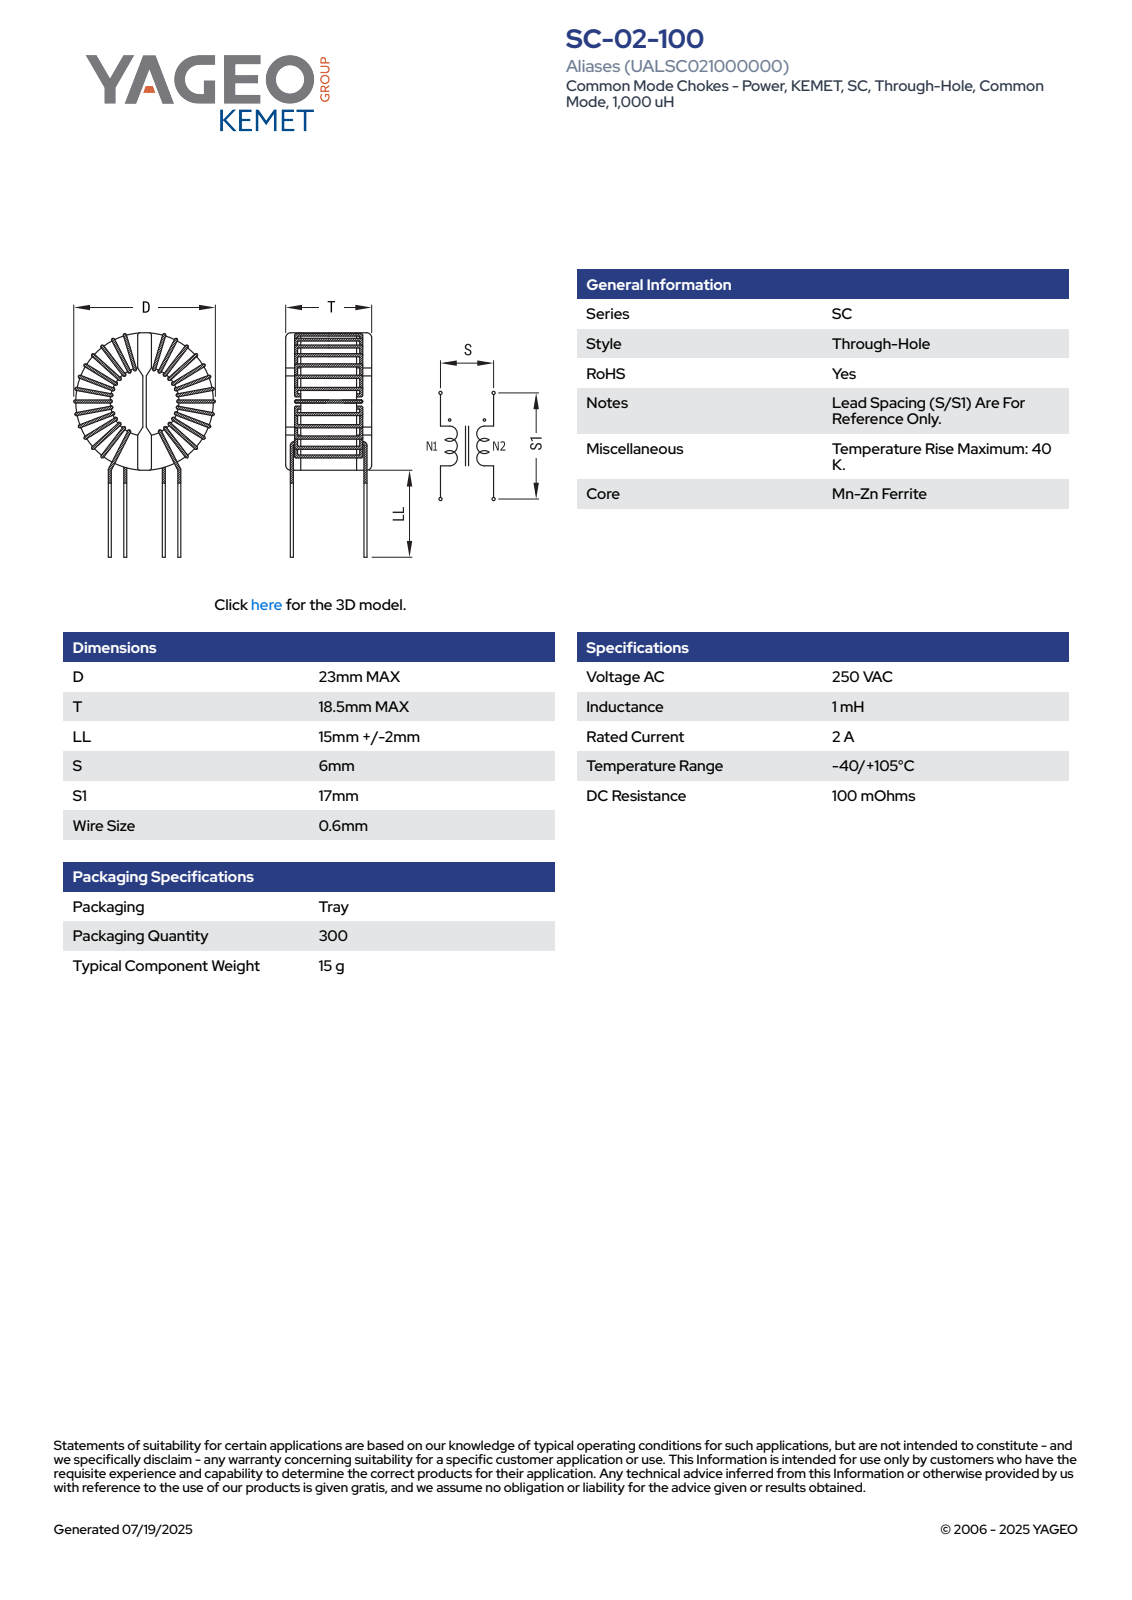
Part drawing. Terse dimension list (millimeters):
name: SC-02-100
written by: SolidWorks 2018 (AUTOMOTIVE_DESIGN)
unit: mm
bodies: 1 solid, 209 faces (62 planar, 79 cylindrical, 68 other)
size: 36.37 × 23 × 18.5
volume: 5 914 mm³; area: 3 520 mm²
bosses: 8× ⌀0.6
rounds: 16× R0.3, 4× R0.2, 1× R2.85, 1× R4.15, 1× R4.65, 1× R4.75, 1× R4.9, 1× R9.25
face distances: 16.3, 1.2, 2, 0.8, 1.1, 3.2, 17.4, 3.48, 12.82, 3.92
